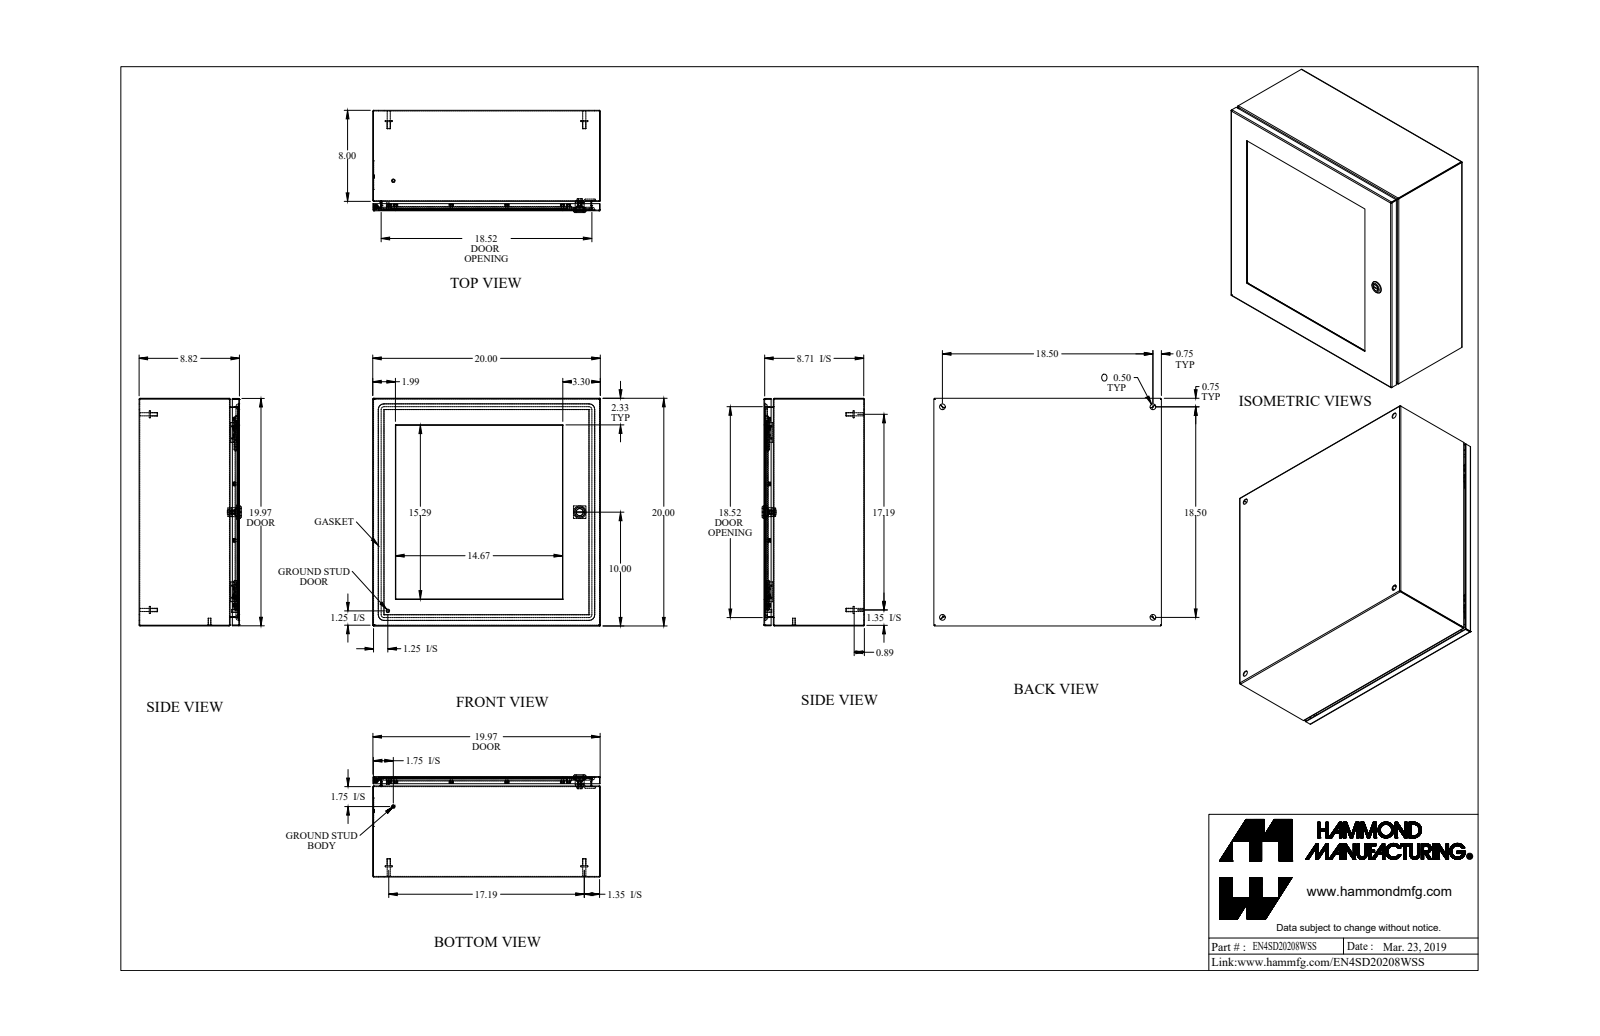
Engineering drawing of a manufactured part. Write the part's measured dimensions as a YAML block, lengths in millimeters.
part_name: "EN4SD20208WSS_Default"
step_written_by: "SolidWorks 2019 (CONFIG_CONTROL_DESIGN)"
units: millimeters
bodies: {solids: 63, faces: 1287, planar: 646, cylindrical: 387, other: 254}
overall_size: [508, 508, 228.1]
volume: 2491000
surface_area: 2337000
round_holes:
  - {diameter: 3.3, count: 16}
  - {diameter: 6.4, count: 16}
  - {diameter: 12.7, count: 5}
  - {diameter: 4.4, count: 1}
  - {diameter: 5, count: 1}
  - {diameter: 6.1, count: 1}
  - {diameter: 6.1, count: 1}
  - {diameter: 9.8, count: 1}
  - {diameter: 16, count: 1}
  - {diameter: 19.5, count: 1}
round_bosses_or_shafts:
  - {diameter: 5.7, count: 17}
  - {diameter: 9.3, count: 16}
  - {diameter: 4.2, count: 16}
  - {diameter: 8, count: 6}
  - {diameter: 15.9, count: 4}
  - {diameter: 7, count: 4}
  - {diameter: 6.4, count: 2}
  - {diameter: 27.9, count: 1}
partial_cylinders:
  - {radius: 0.7, count: 21}
  - {radius: 2.2, count: 21}
  - {radius: 4.8, count: 12}
  - {radius: 3.2, count: 10}
  - {radius: 0.2, count: 4}
  - {radius: 0.4, count: 4}
  - {radius: 1.6, count: 4}
  - {radius: 2.2, count: 4}
face_to_face_distances: [1.4, 506.6, 222.6, 221.2, 505.1, 508, 6.4, 214.8, 216.3, 7.8]
hole_center_spacings: [248.4, 414.9, 124.2, 124.2, 124.2, 124.2, 262.2, 418.4]
